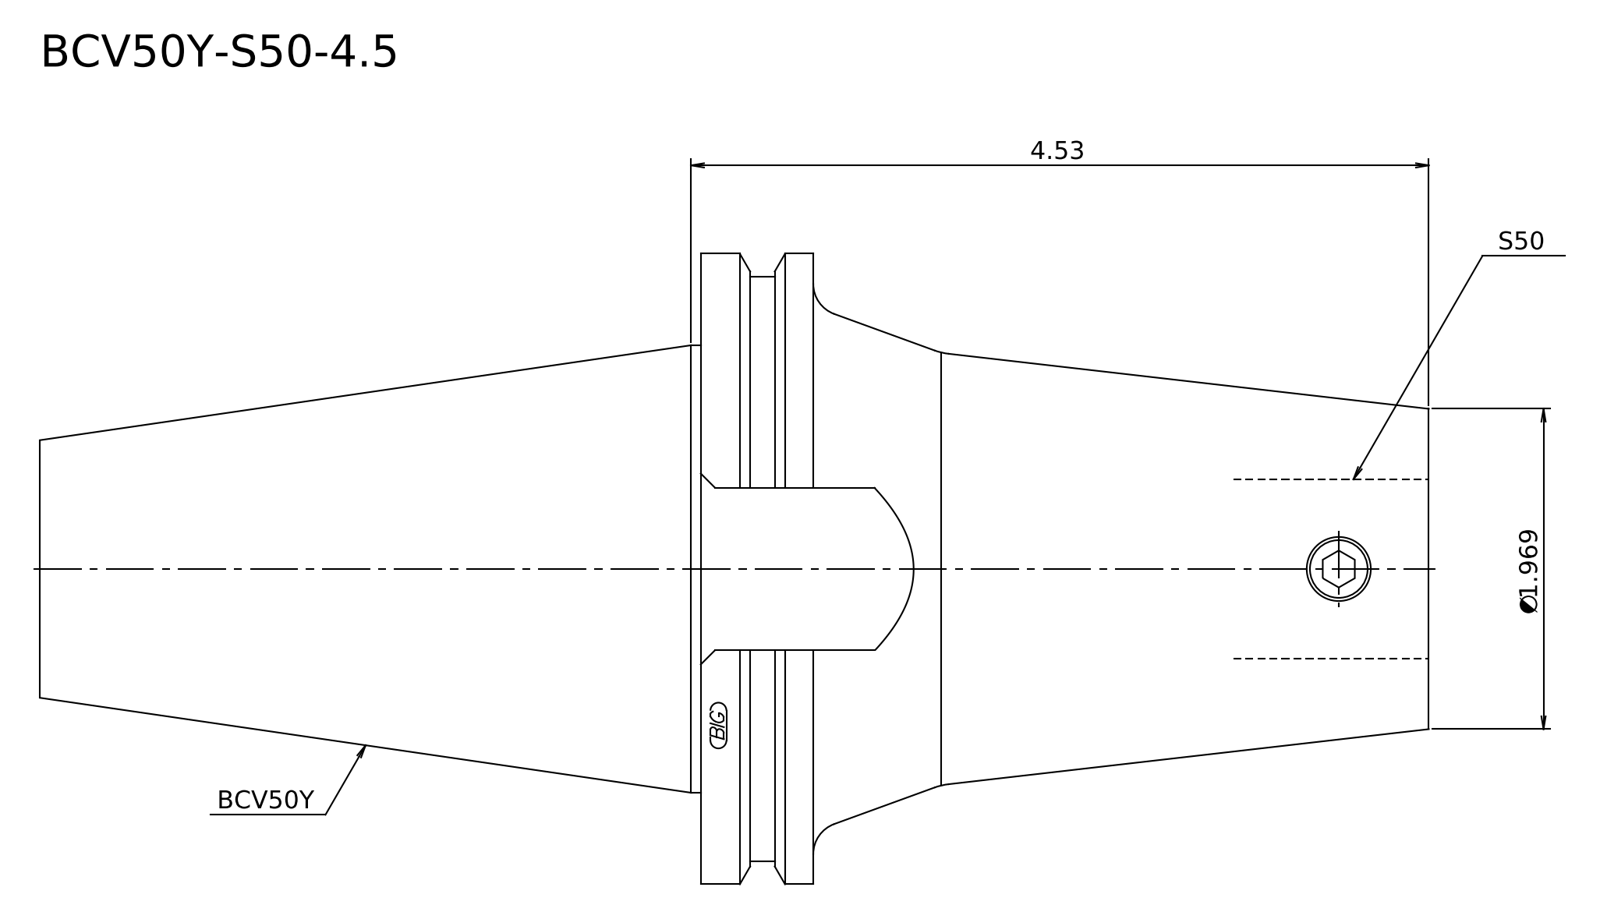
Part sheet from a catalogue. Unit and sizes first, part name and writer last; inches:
Units: inches
Overall size (bounding box): 8.531 × 3.875 × 3.875
Round bosses / shafts (diameter × count): ⌀3.875 ×1, ⌀3.594 ×1, ⌀2.75 ×1
Main face-to-face distances: 4.472, 3.781, 0.691, 8.531, 4.75, 4.059, 4.169, 0.388, 0.303, 4.362
Volume: 41.43 in³ · Surface area: 82.1 in²
Bodies: 1 solid, 16 faces (6 planar, 4 cylindrical, 6 other)
STEP written by: Kubotek KeyCreator 2011 V10.0.2 (22737) (automotive_design)
